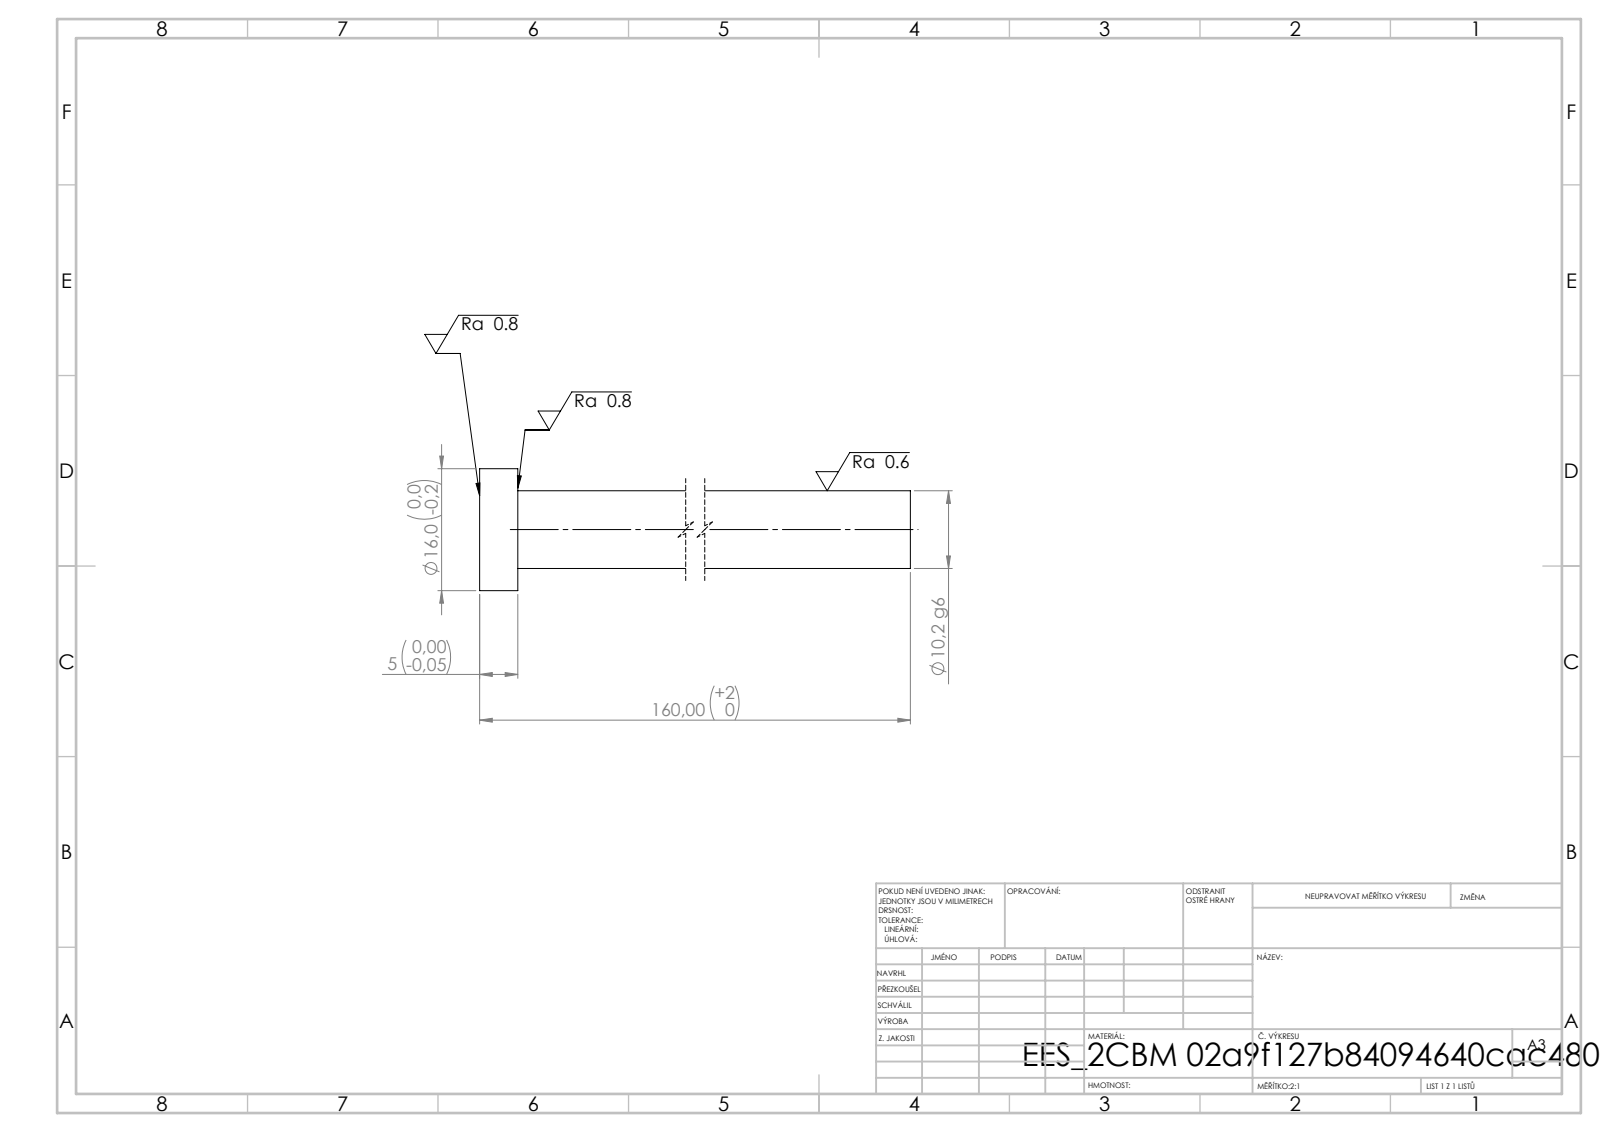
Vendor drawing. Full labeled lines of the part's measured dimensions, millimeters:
STEP written by: SolidWorks 2019 (CONFIG_CONTROL_DESIGN)
Units: millimetres
Bodies: 1 solid, 7 faces (3 planar, 4 cylindrical, 0 other)
Overall size (bounding box): 160 × 16 × 16
Volume: 13 671 mm³ · Surface area: 5 620 mm²
Round bosses / shafts (diameter × count): ⌀16 ×1, ⌀10.2 ×1
Main face-to-face distances: 5, 160, 155
